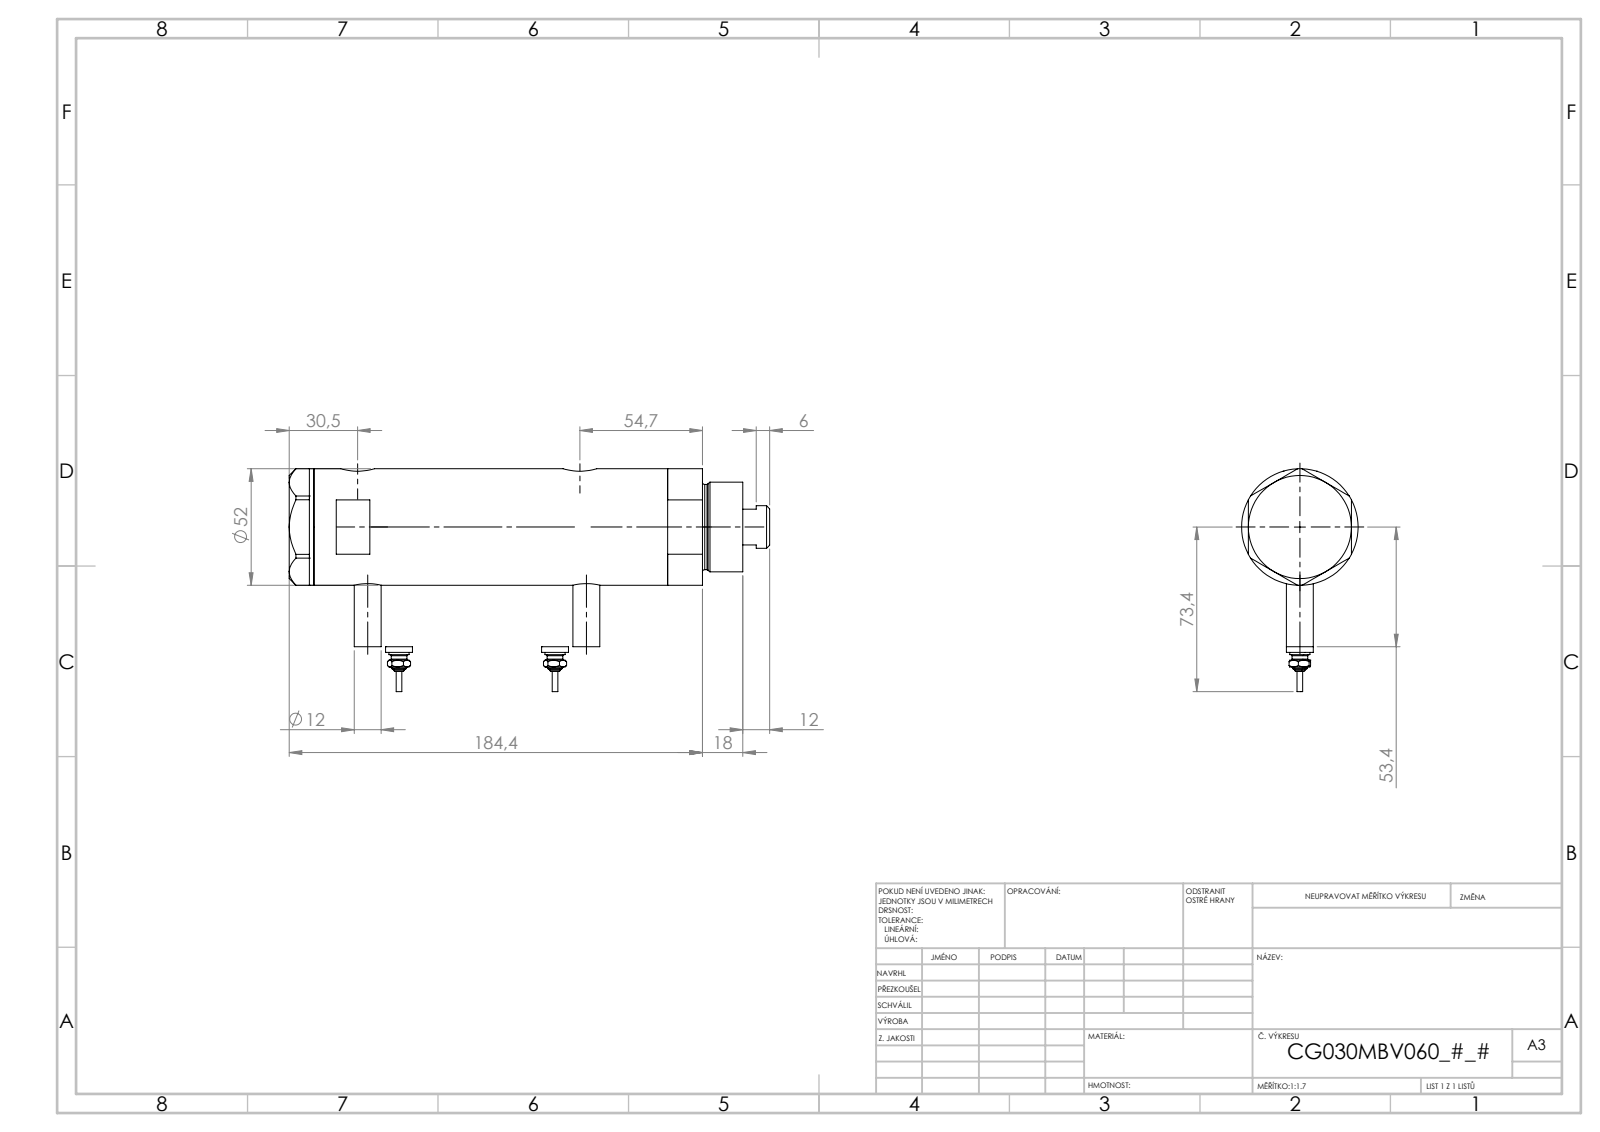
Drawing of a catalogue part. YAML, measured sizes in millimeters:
part_name: "V270CG_SWITCH; V270CG_FRONT; V270CG_VC; V270CG_MIDDLE (+1 more)"
step_written_by: "SolidWorks 2019 (CONFIG_CONTROL_DESIGN)"
units: millimeters
bodies: {solids: 6, faces: 246, planar: 95, cylindrical: 77, other: 74}
overall_size: [209.02, 84.3, 52]
volume: 374236
surface_area: 86263
round_holes:
  - {diameter: 5, count: 2}
  - {diameter: 9.73, count: 2}
  - {diameter: 12.5, count: 2}
  - {diameter: 15, count: 2}
  - {diameter: 6.5, count: 1}
  - {diameter: 20, count: 1}
  - {diameter: 21.5, count: 1}
  - {diameter: 30, count: 1}
  - {diameter: 33, count: 1}
  - {diameter: 44, count: 1}
round_bosses_or_shafts:
  - {diameter: 12, count: 3}
  - {diameter: 9, count: 2}
  - {diameter: 7, count: 2}
  - {diameter: 4.34, count: 2}
  - {diameter: 2.4, count: 2}
  - {diameter: 52, count: 1}
  - {diameter: 40, count: 1}
  - {diameter: 38, count: 1}
face_to_face_distances: [23.8, 124.55, 46, 11, 11.01, 113.55, 113.54, 160.95, 149.95, 149.94]
hole_center_spacings: [2.9, 4.5, 86.75, 89.65, 91.25, 94.15, 2.89, 2.91]
